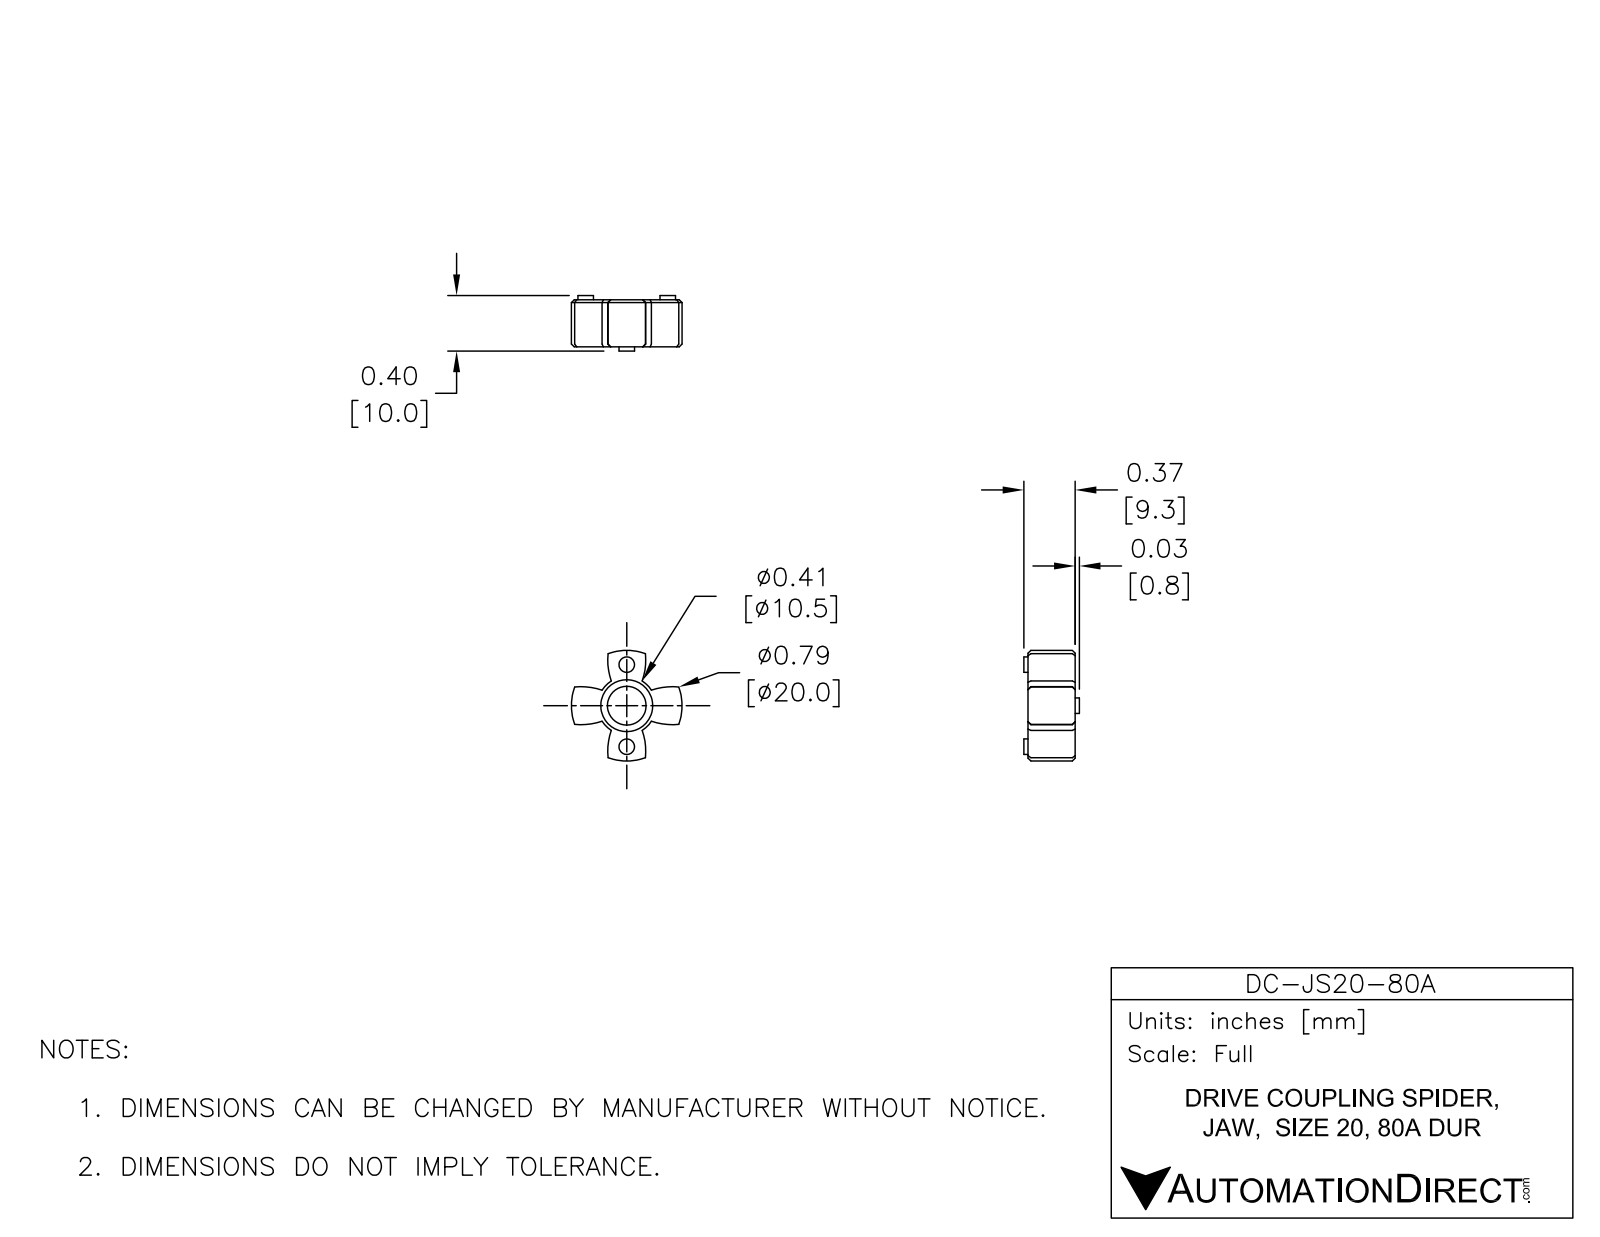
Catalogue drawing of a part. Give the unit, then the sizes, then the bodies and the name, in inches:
Units: inches
Overall size (bounding box): 0.786 × 0.786 × 0.395
Round holes (diameter × count): ⌀0.275 ×1
Round bosses / shafts (diameter × count): ⌀0.11 ×4
Partial cylindrical surfaces — rounded edges, fillets, slot ends (radius × count): R0.46 ×4, R0.207 ×1, R0.393 ×1
Main face-to-face distances: 0.335, 0.125, 0.21, 0.085, 0.03, 0.155, 0.24, 0.365, 0.395
Volume: 0.093 in³ · Surface area: 1.821 in²
Bodies: 1 solid, 81 faces (8 planar, 31 cylindrical, 42 other)
Part name (STEP PRODUCT): DC-JS20-80A
STEP written by: SolidWorks 2015 (AUTOMOTIVE_DESIGN)
